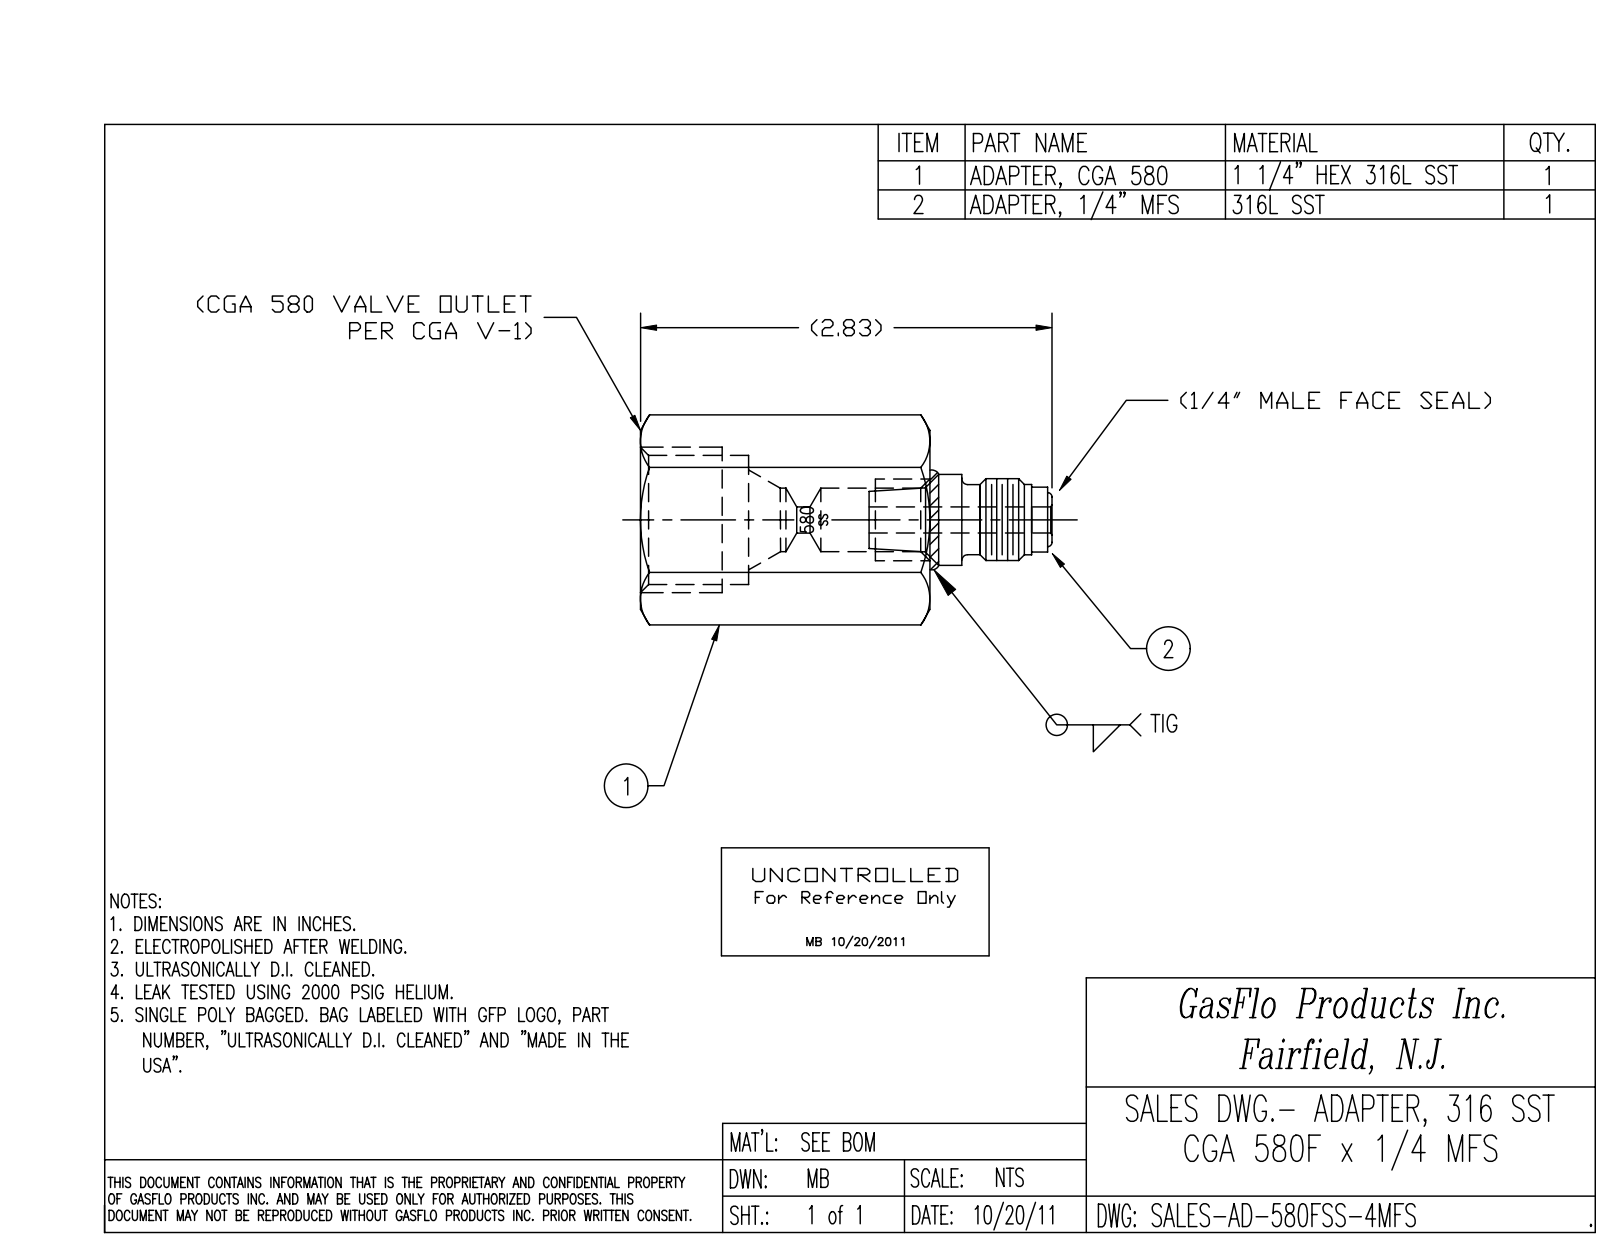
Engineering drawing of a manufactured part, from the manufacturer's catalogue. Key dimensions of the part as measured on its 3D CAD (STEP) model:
Part name (STEP PRODUCT): PRT-001130; AD-580FSS-4MFS; PRT-001202
STEP written by: SolidWorks 2018 (CONFIG_CONTROL_DESIGN)
Units: inches
Bodies: 2 solids, 124 faces (22 planar, 48 cylindrical, 54 other)
Overall size (bounding box): 2.809 × 1.443 × 1.25
Volume: 2.242 in³ · Surface area: 19.6 in²
Round holes (diameter × count): ⌀0.179 ×1, ⌀0.187 ×1, ⌀0.231 ×1, ⌀0.422 ×1, ⌀0.422 ×1, ⌀0.892 ×1
Round bosses / shafts (diameter × count): ⌀0.625 ×1, ⌀0.557 ×1, ⌀0.481 ×1, ⌀0.444 ×1, ⌀0.394 ×1
Main face-to-face distances: 1.25, 1.25, 2, 1.313, 0.687, 0.448, 0.865, 1.552, 0.189, 0.637
